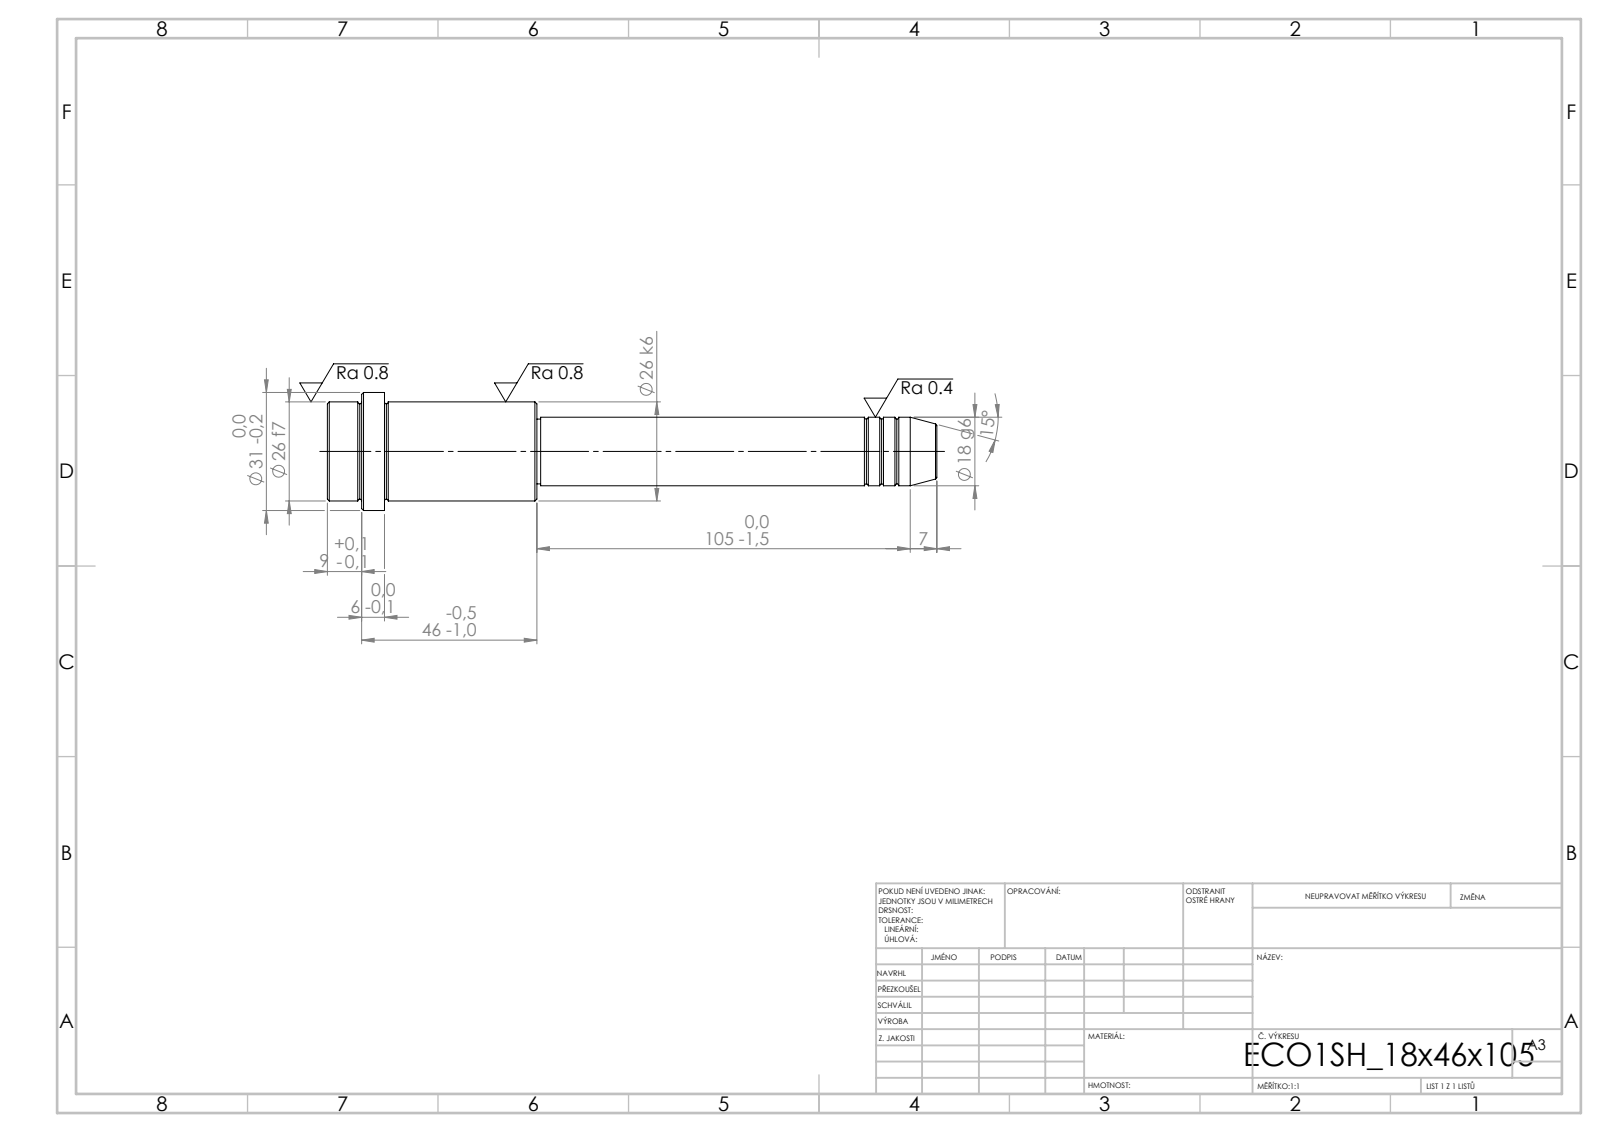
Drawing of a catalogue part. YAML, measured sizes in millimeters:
step_written_by: "SolidWorks 2019 (CONFIG_CONTROL_DESIGN)"
units: millimeters
bodies: {solids: 1, faces: 52, planar: 6, cylindrical: 16, other: 30}
overall_size: [160, 31, 31]
volume: 56729
surface_area: 12054
round_bosses_or_shafts:
  - {diameter: 31, count: 1}
  - {diameter: 26, count: 1}
  - {diameter: 18, count: 1}
  - {diameter: 17, count: 1}
face_to_face_distances: [55, 40, 15, 46, 6, 9, 105, 145, 151, 160]
